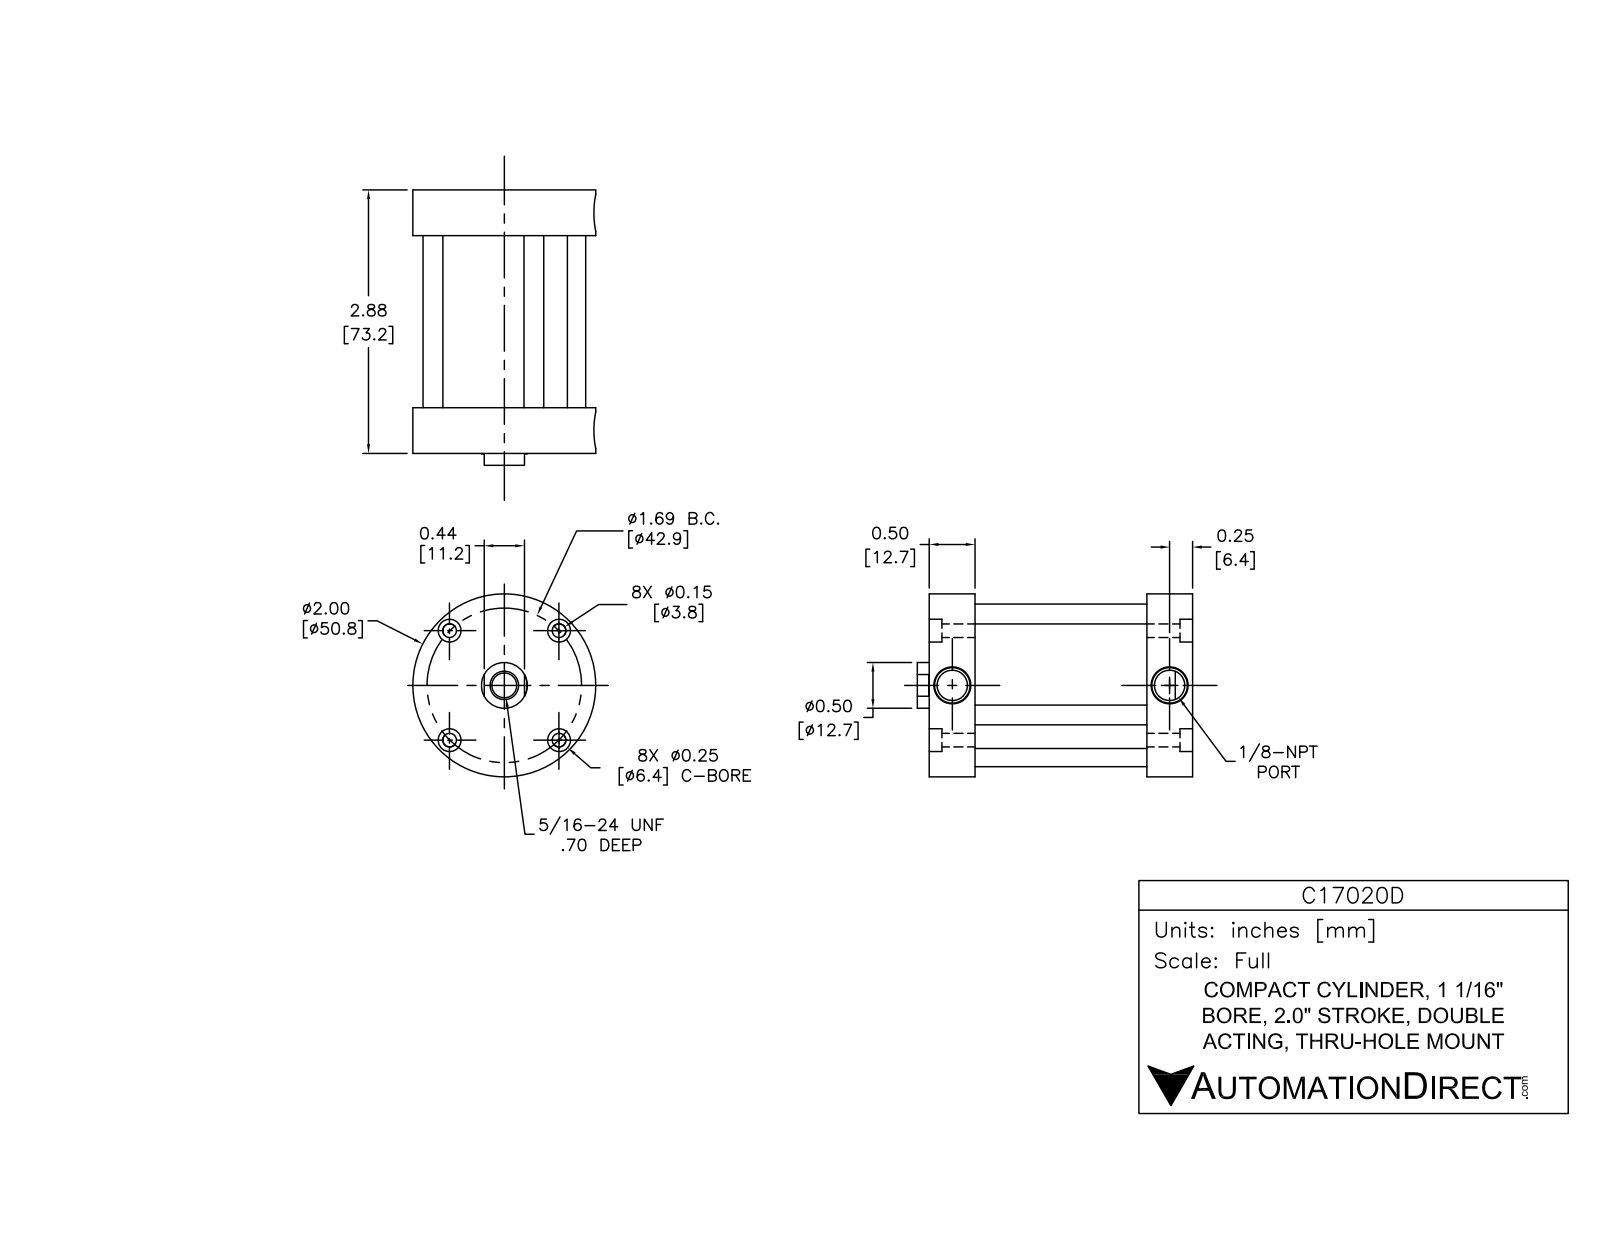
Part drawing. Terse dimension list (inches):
name: C17020D; C17020D-rod_part; C17020D-FO1_BM_rod; C17020D-FO1_BM_heads (2) (+3 more)
written by: SolidWorks 2014 (AUTOMOTIVE_DESIGN)
unit: in
bodies: 9 solids, 165 faces (49 planar, 98 cylindrical, 18 other)
size: 3.01 × 2 × 2
volume: 3.85 in³; area: 55.89 in²
holes: 4× ⌀0.136, 4× ⌀0.156, 4× ⌀0.25, 2× ⌀0.125, 1× ⌀0.267, 1× ⌀0.5, 1× ⌀0.502, 1× ⌀1.062, 1× ⌀1.122
bosses: 4× ⌀0.272, 1× ⌀2
face distances: 0.5, 2.38, 0.282, 2.598, 0.218, 2.098, 2.88, 1.88, 2.316, 0.598
hole spacings: 0.33, 0.845, 0.845, 0.939, 1.195, 1.195, 1.406, 1.657
